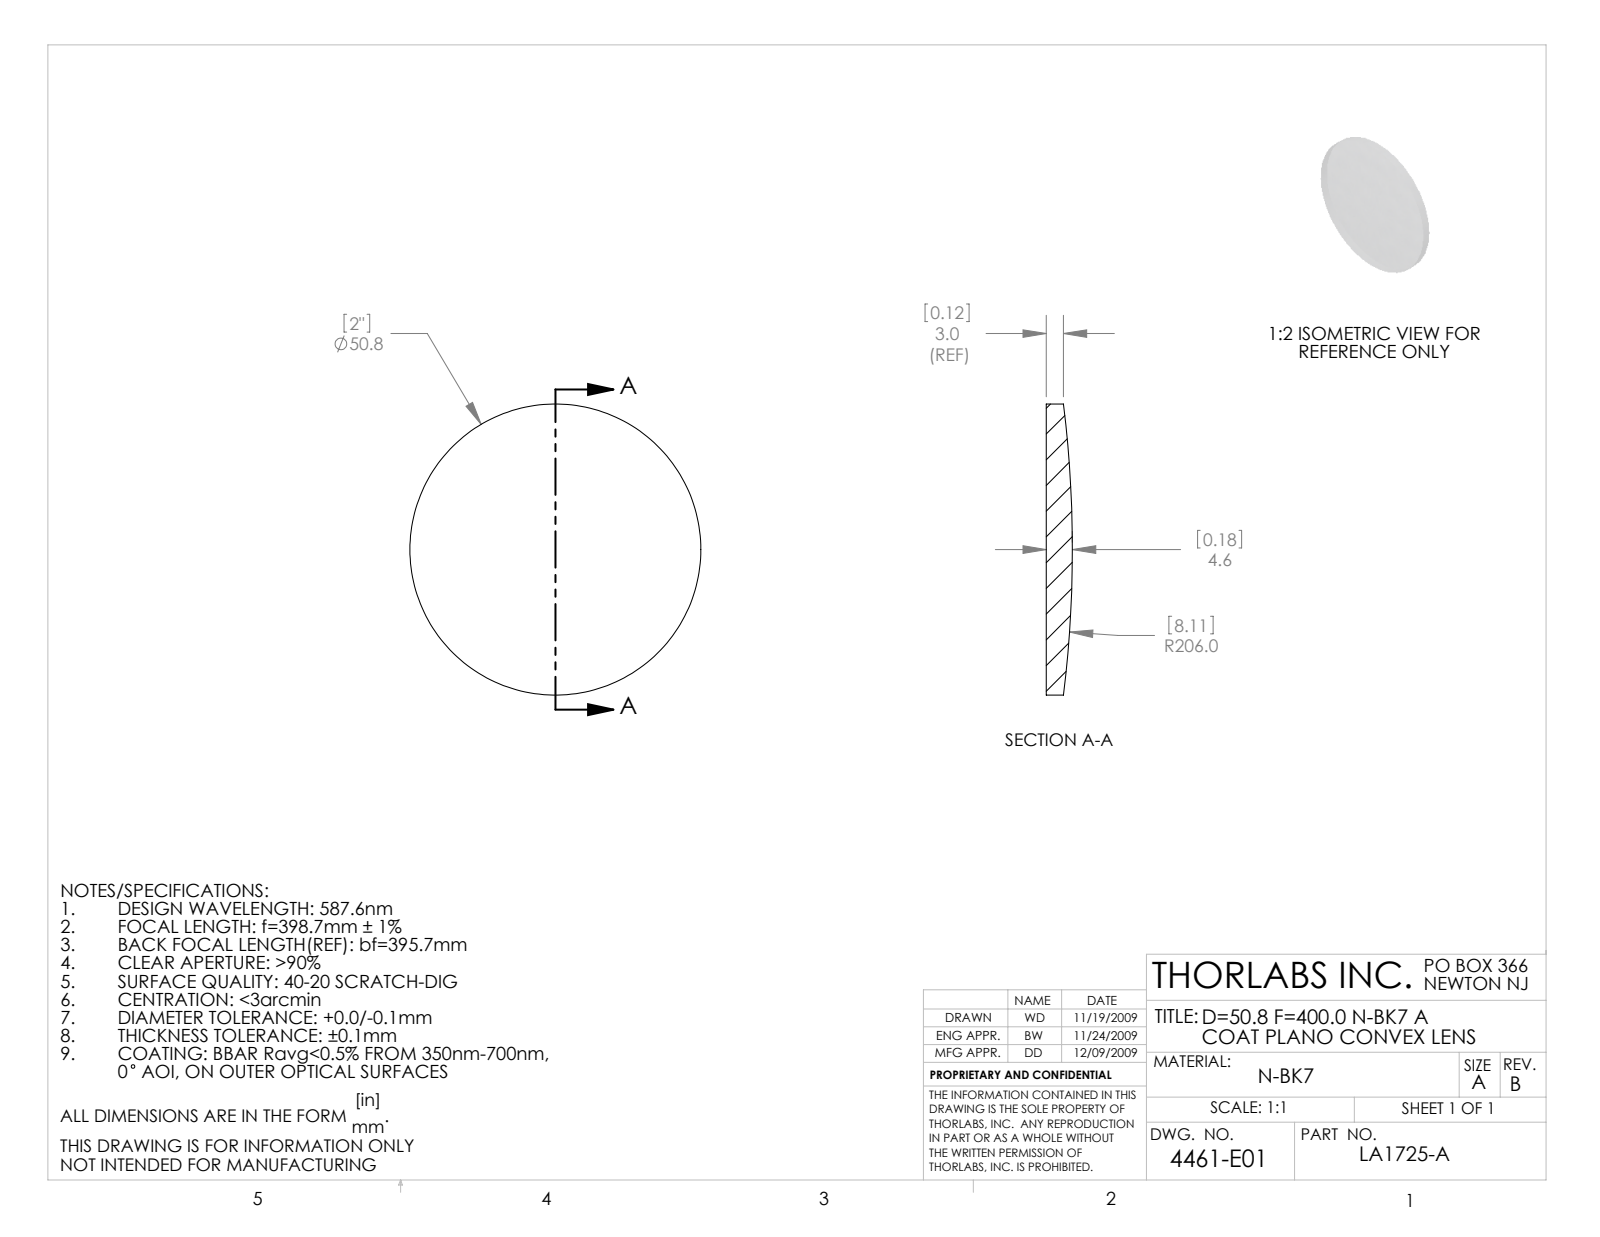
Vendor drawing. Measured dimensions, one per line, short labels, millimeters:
name: 4461-E0W
written by: SolidWorks 2009 (AUTOMOTIVE_DESIGN)
unit: mm
bodies: 1 solid, 5 faces (1 planar, 2 cylindrical, 2 other)
size: 50.8 × 50.8 × 4.57
volume: 7 672 mm³; area: 4 540 mm²
bosses: 1× ⌀50.8
